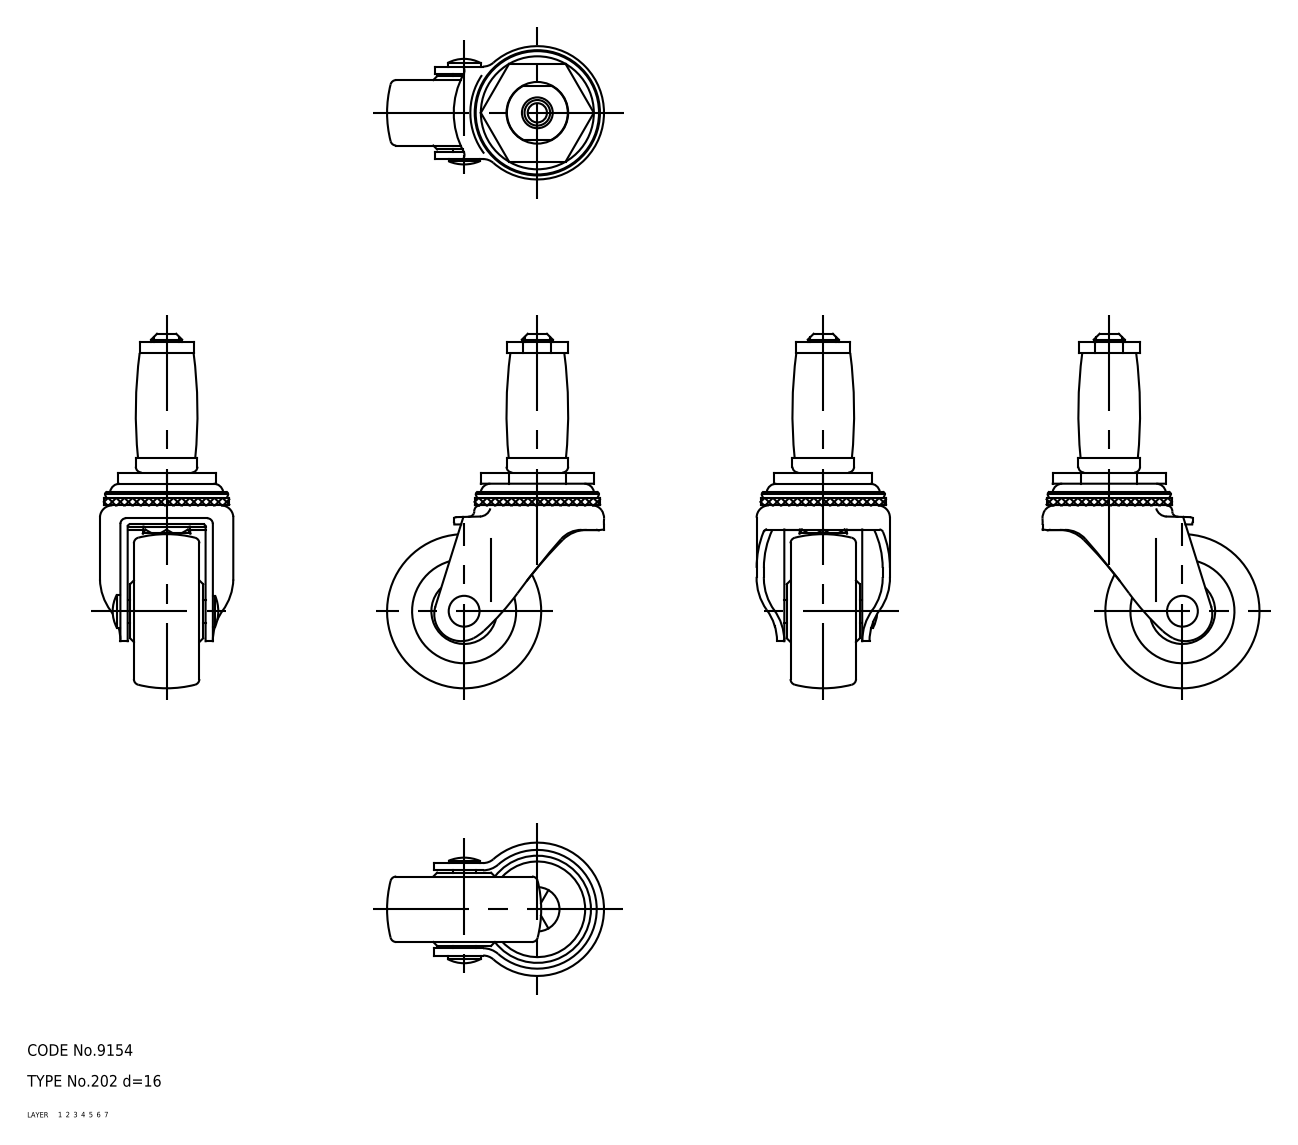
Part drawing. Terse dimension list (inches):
name: wheel; main shaft; axle; No_202_d16_21017_36
written by: CADfix (AUTOMOTIVE_DESIGN)
unit: in
bodies: 4 solids, 179 faces (0 planar, 0 cylindrical, 179 other)
size: 3.622 × 2.217 × 1.362
volume: 2.441 in³; area: 24.86 in²
